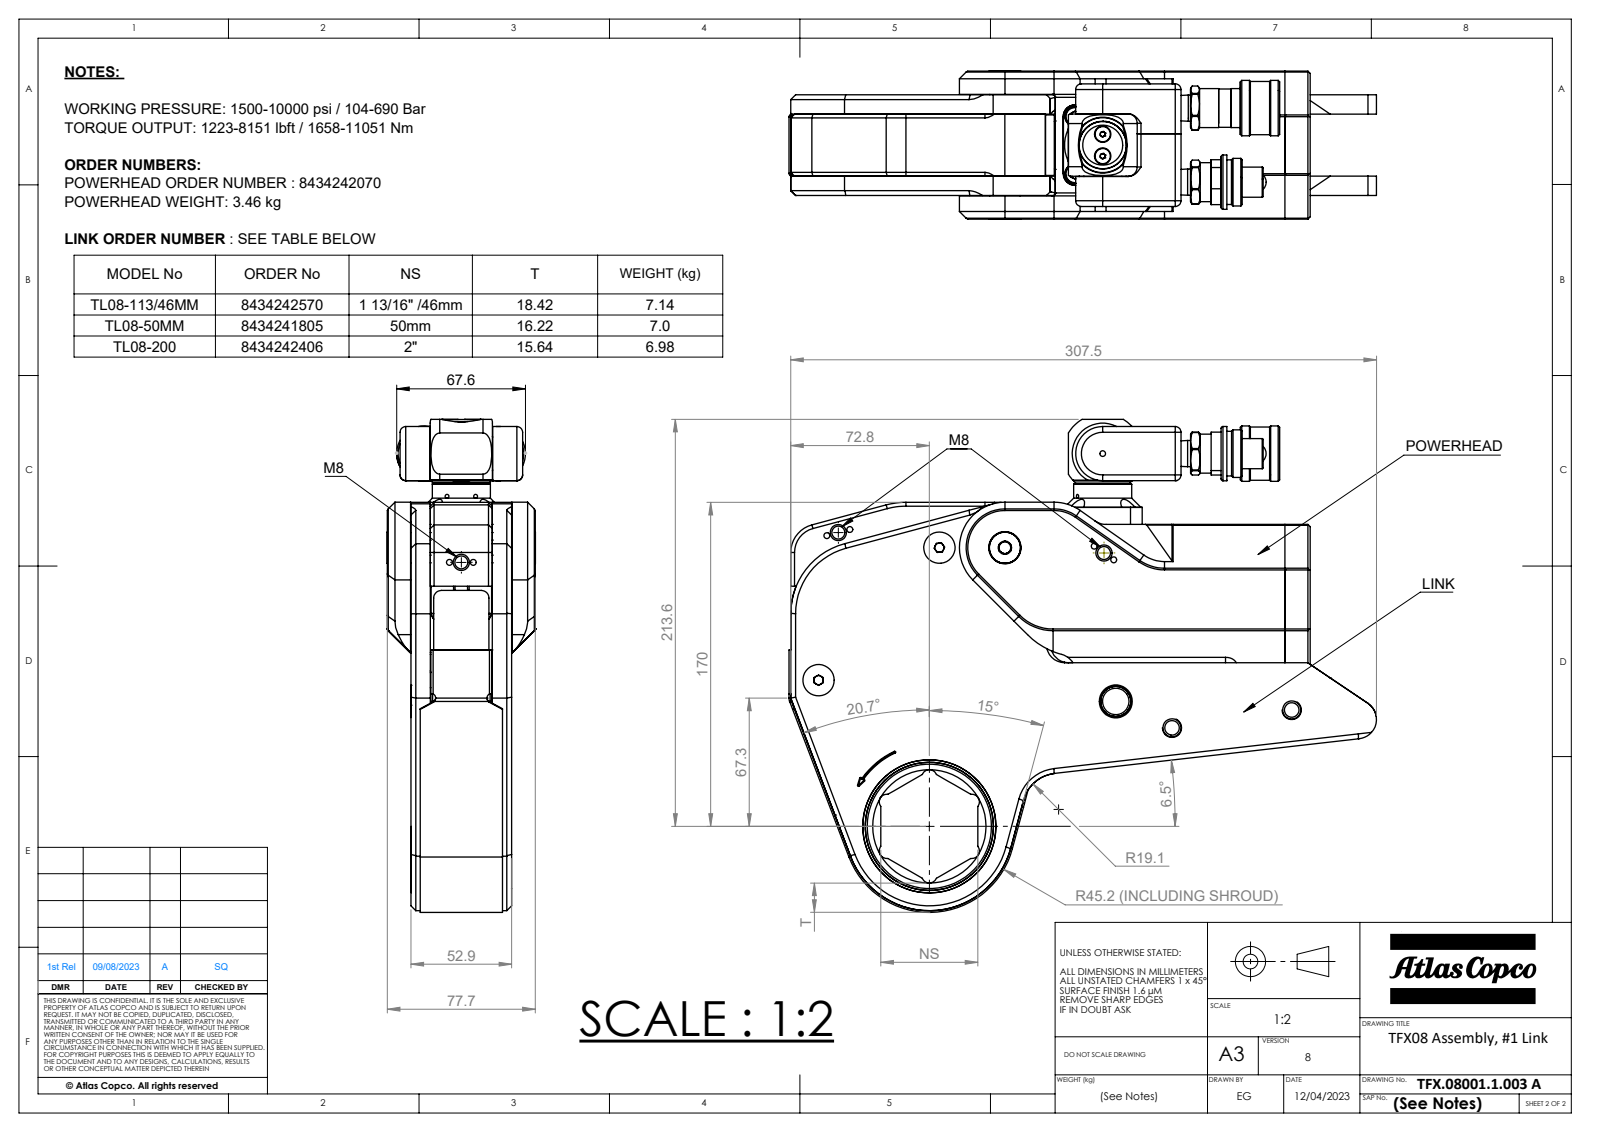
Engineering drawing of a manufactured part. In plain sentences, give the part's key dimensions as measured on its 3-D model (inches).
The part is named "RTX-08 SIDEPLATE ASSY [RH ONLY]_RTX.08001.1.002; TFX.08000.0.004A_No Engraving; TFX08 ToolFit - PowerHead [CoAx]; STP.00001.0.010A_STP.00001.0.010A (+8 more)". Its 3-D file was written by "SolidWorks 2023 (AUTOMOTIVE_DESIGN)". It is 19 solids with 1496 faces: 621 planar, 431 cylindrical and 444 other. Overall it measures 12.144 by 10.371 by 3.065 inches. Its volume is 56.7 cubic inches and its surface area 556.9 square inches. Round holes: 8 of diameter 0.551, 6 of diameter 0.122, 4 of diameter 0.404, 3 of diameter 0.268, 3 of diameter 0.397, 2 of diameter 0.079, 2 of diameter 0.313, 2 of diameter 0.319, 2 of diameter 0.438, 2 of diameter 0.5, 2 of diameter 0.628, 1 of diameter 0.162. Round bosses or shafts: 8 of diameter 0.512, 3 of diameter 0.781, 3 of diameter 0.648, 3 of diameter 0.375, 3 of diameter 0.313, 2 of diameter 0.394, 2 of diameter 0.315, 1 of diameter 3.484. Partial cylindrical surfaces (rounded edges, fillets, slot ends): 10 of radius 0.157, 7 of radius 0.031, 6 of radius 0.039, 5 of radius 0.094, 5 of radius 0.394, 4 of radius 0.063, 4 of radius 0.079, 4 of radius 0.239. The main face-to-face distances are 0.4, 1.682, 1.282, 2.082, 2.17, 0.887, 0.487, 2.169, 2.569, 3.057. The hole center spacings are 0.246, 0.824, 0.904, 1.67, 3.641, 6.249, 8.934, 9.823.
